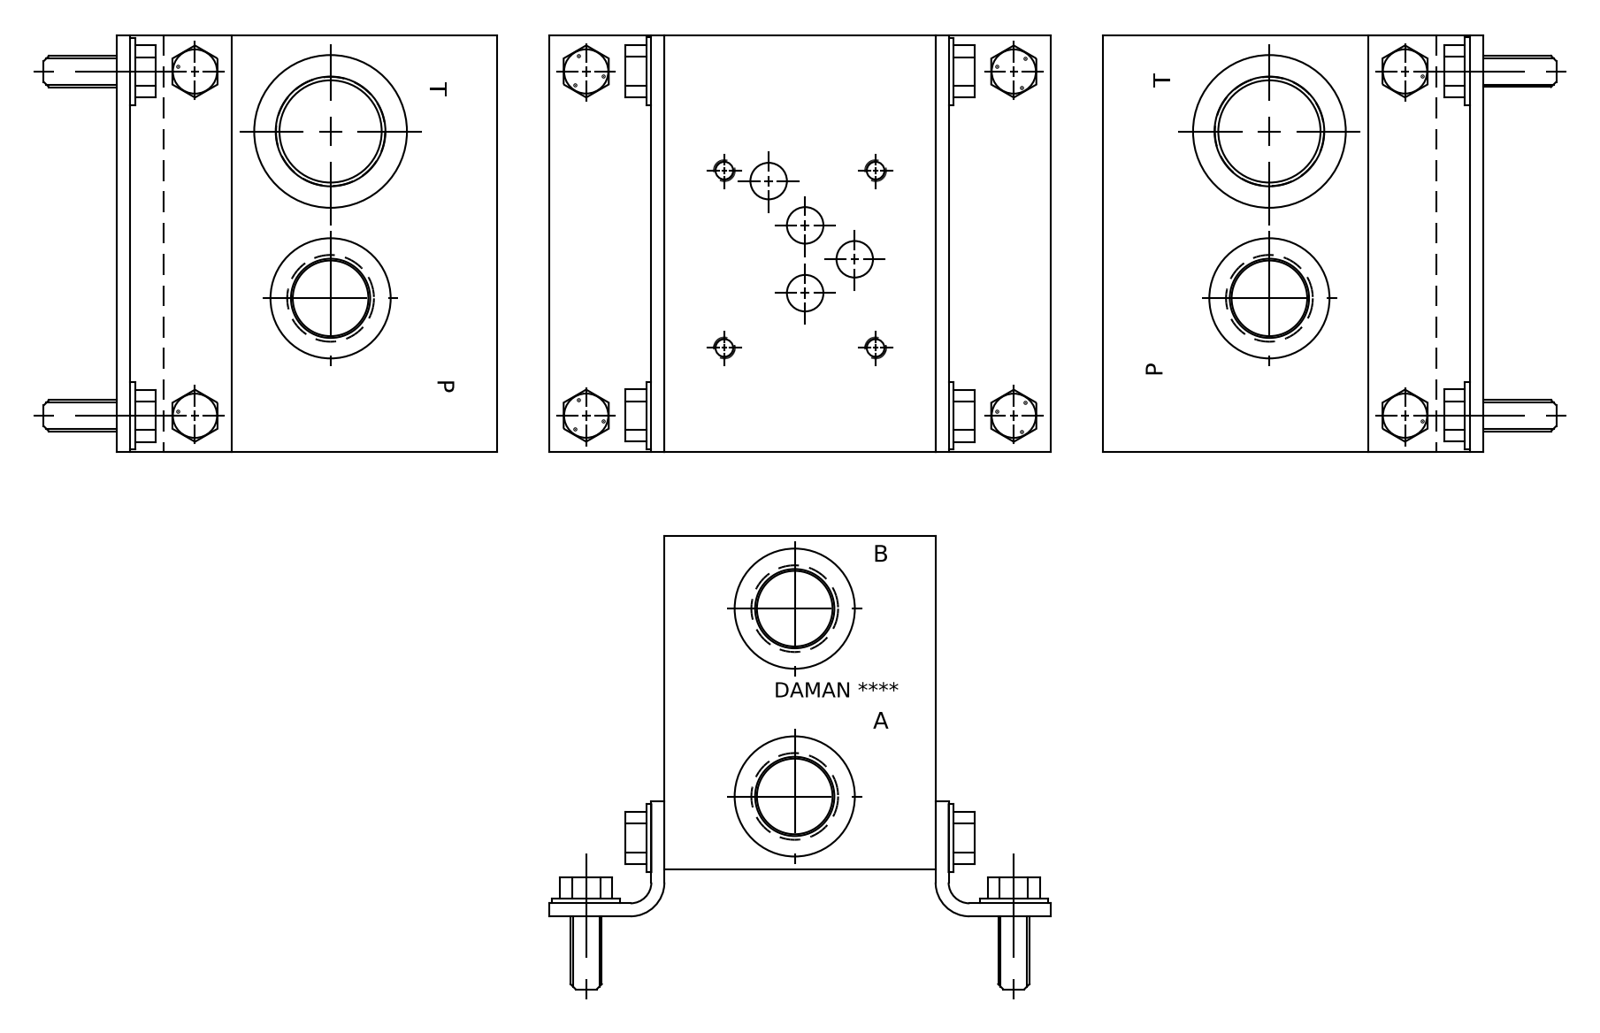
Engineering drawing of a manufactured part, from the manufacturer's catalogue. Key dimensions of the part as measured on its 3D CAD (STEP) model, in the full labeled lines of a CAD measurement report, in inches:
Part name (STEP PRODUCT): Part_AD05HP013B_3D
STEP written by: Autodesk Inventor 2021 (AUTOMOTIVE_DESIGN)
Units: inches
Bodies: 1 solid, 513 faces (320 planar, 44 cylindrical, 149 other)
Overall size (bounding box): 5 × 4 × 3.25
Volume: 56.98 in³ · Surface area: 131.4 in²
Round holes (diameter × count): ⌀0.197 ×4, ⌀0.236 ×4, ⌀0.906 ×3, ⌀0.961 ×3, ⌀1.045 ×3, ⌀1.461 ×3, ⌀0.335 ×2, ⌀0.394 ×2, ⌀0.437 ×2, ⌀0.438 ×2, ⌀1.125 ×1, ⌀1.206 ×1
Main face-to-face distances: 4, 3.25, 5, 0.031, 3.219, 3.188, 4.969, 0.704, 0.673, 0.814
Hole centre spacings: 0.72, 1.171, 1.813, 2.793, 0.546, 0.689, 0.812, 1.068
